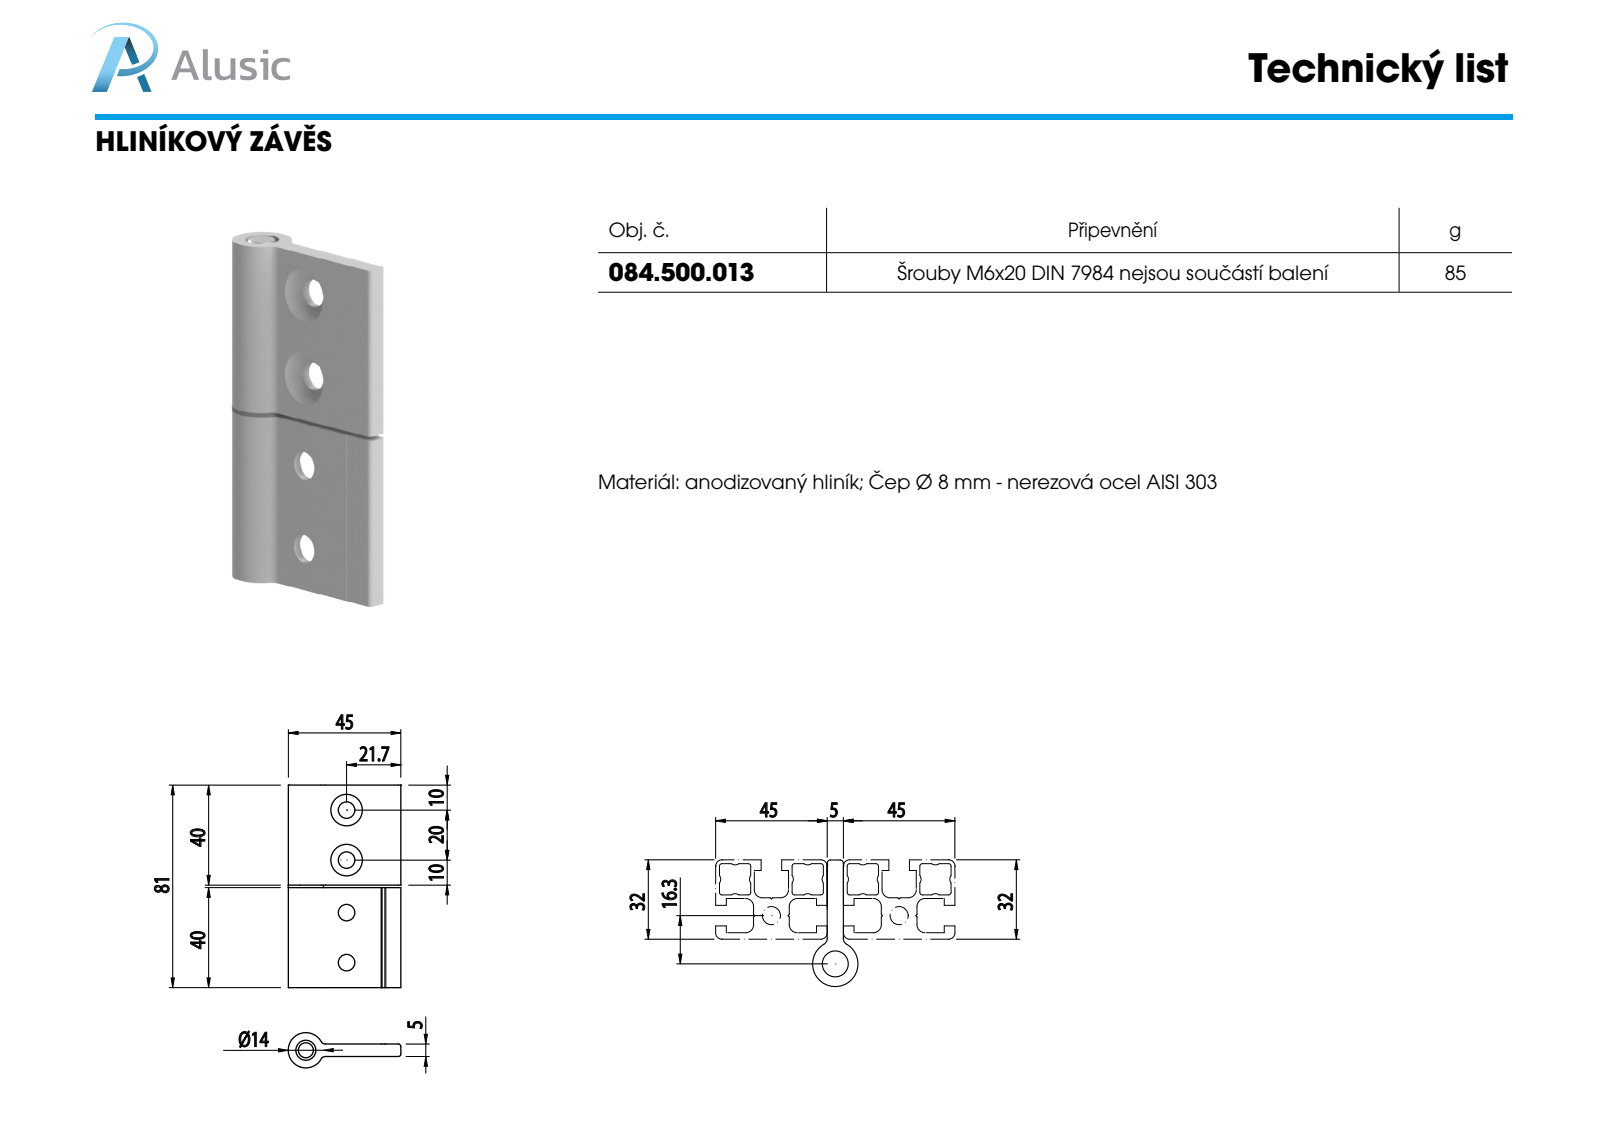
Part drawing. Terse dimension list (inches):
name: 084.500.013; PERNO CERNIERA_084.500.001.B; 084.500.001.C; 084.500.013L
written by: SolidWorks 2011 (CONFIG_CONTROL_DESIGN)
unit: in
bodies: 4 solids, 188 faces (142 planar, 34 cylindrical, 12 other)
size: 3.189 × 1.774 × 0.555
volume: 1.448 in³; area: 21.66 in²
holes: 4× ⌀0.26, 1× ⌀0.315, 1× ⌀0.319
bosses: 1× ⌀0.555, 1× ⌀0.551
rounds: 2× R0.008, 2× R0.039, 2× R0.079
face distances: 0.197, 1.575, 1.614, 0.039, 3.189, 0.241, 0.241, 0.128, 1.358, 0.217
hole spacings: 0.787, 1.614, 0.827, 2.402
